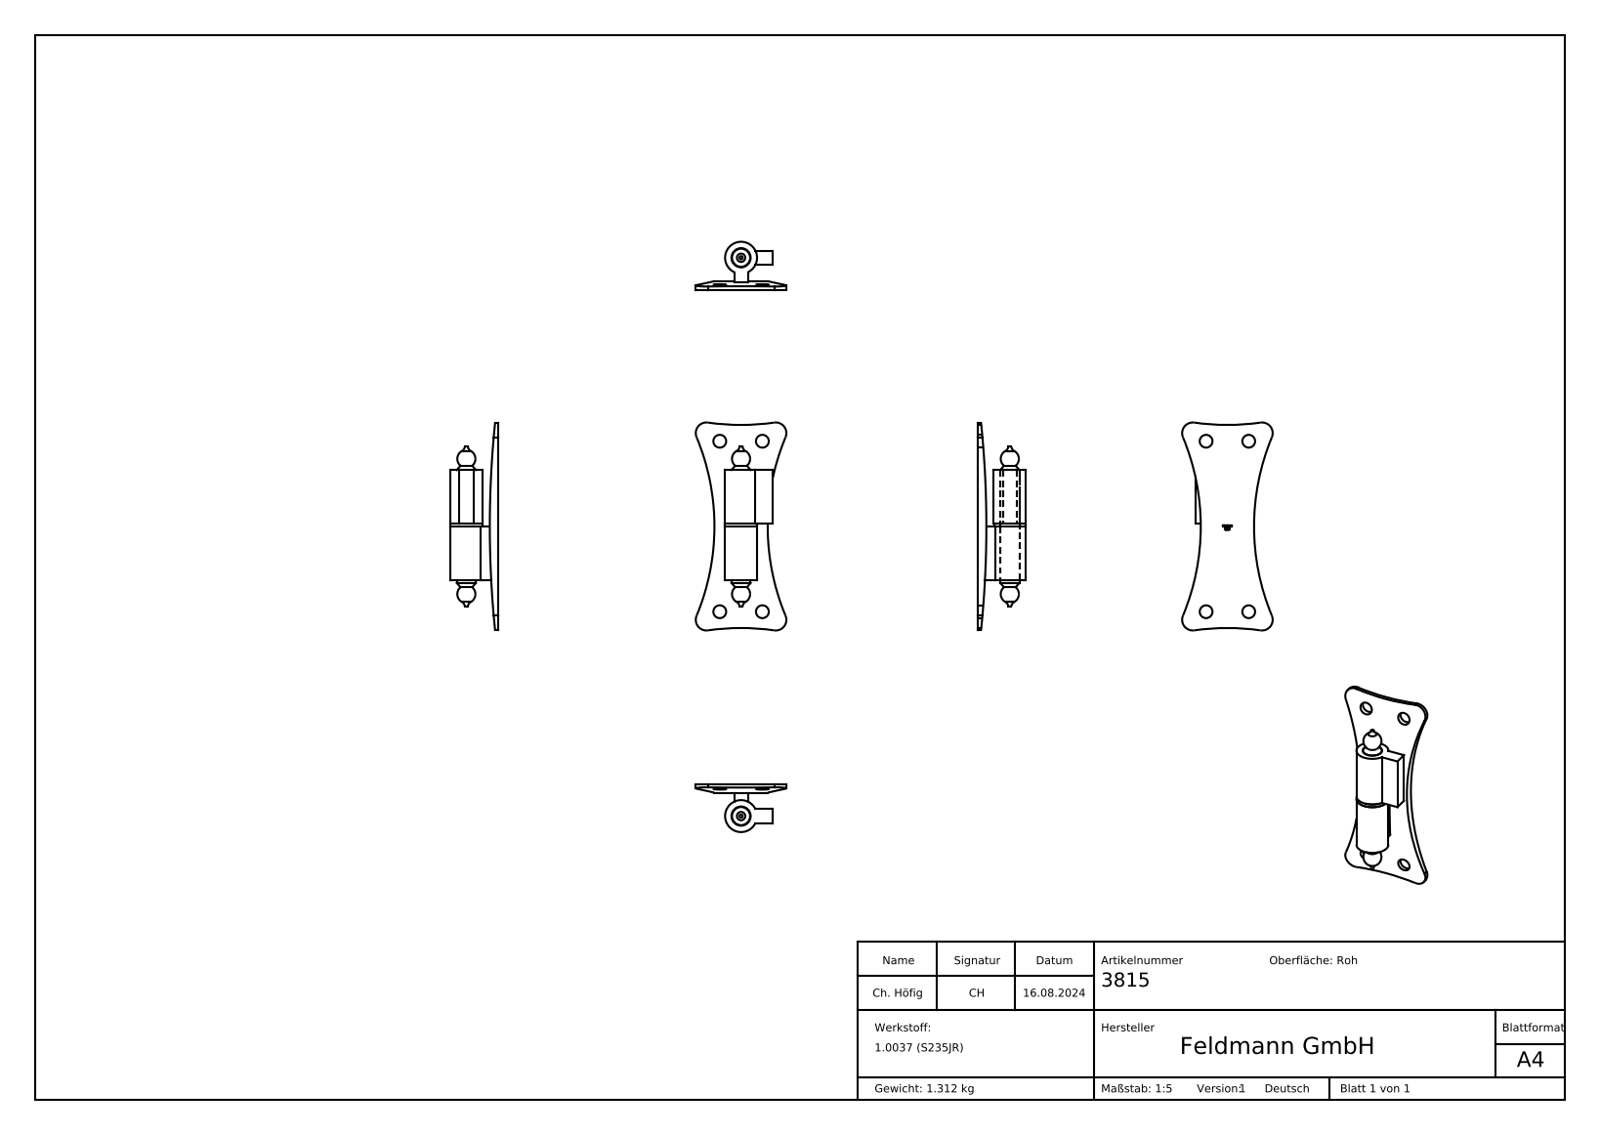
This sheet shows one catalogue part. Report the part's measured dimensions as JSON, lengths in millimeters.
{"part_name": "3815 Teil1_3815 Teil1; 3815 Teil2_3815 Teil2; 3815; 3815 Teil3_3815 Teil3", "step_written_by": "SolidWorks 2018 (CONFIG_CONTROL_DESIGN)", "units": "millimeters", "bodies": {"solids": 5, "faces": 216, "planar": 102, "cylindrical": 21, "other": 93}, "overall_size": [195.2, 85, 45], "volume_mm3": 168131, "surface_area_mm2": 56062, "round_holes": [[12, 4], [18, 1], [18.25, 1]], "round_bosses_or_shafts": [[30, 1], [29.8, 1]], "partial_cylinders_radius": [[10, 4], [218, 2], [220.45, 2], [955.08, 1]], "face_to_face_distances": [23.5, 36.5, 13, 50, 53, 3, 103, 75, 25, 78], "hole_center_spacings": [40, 160, 164.92]}
